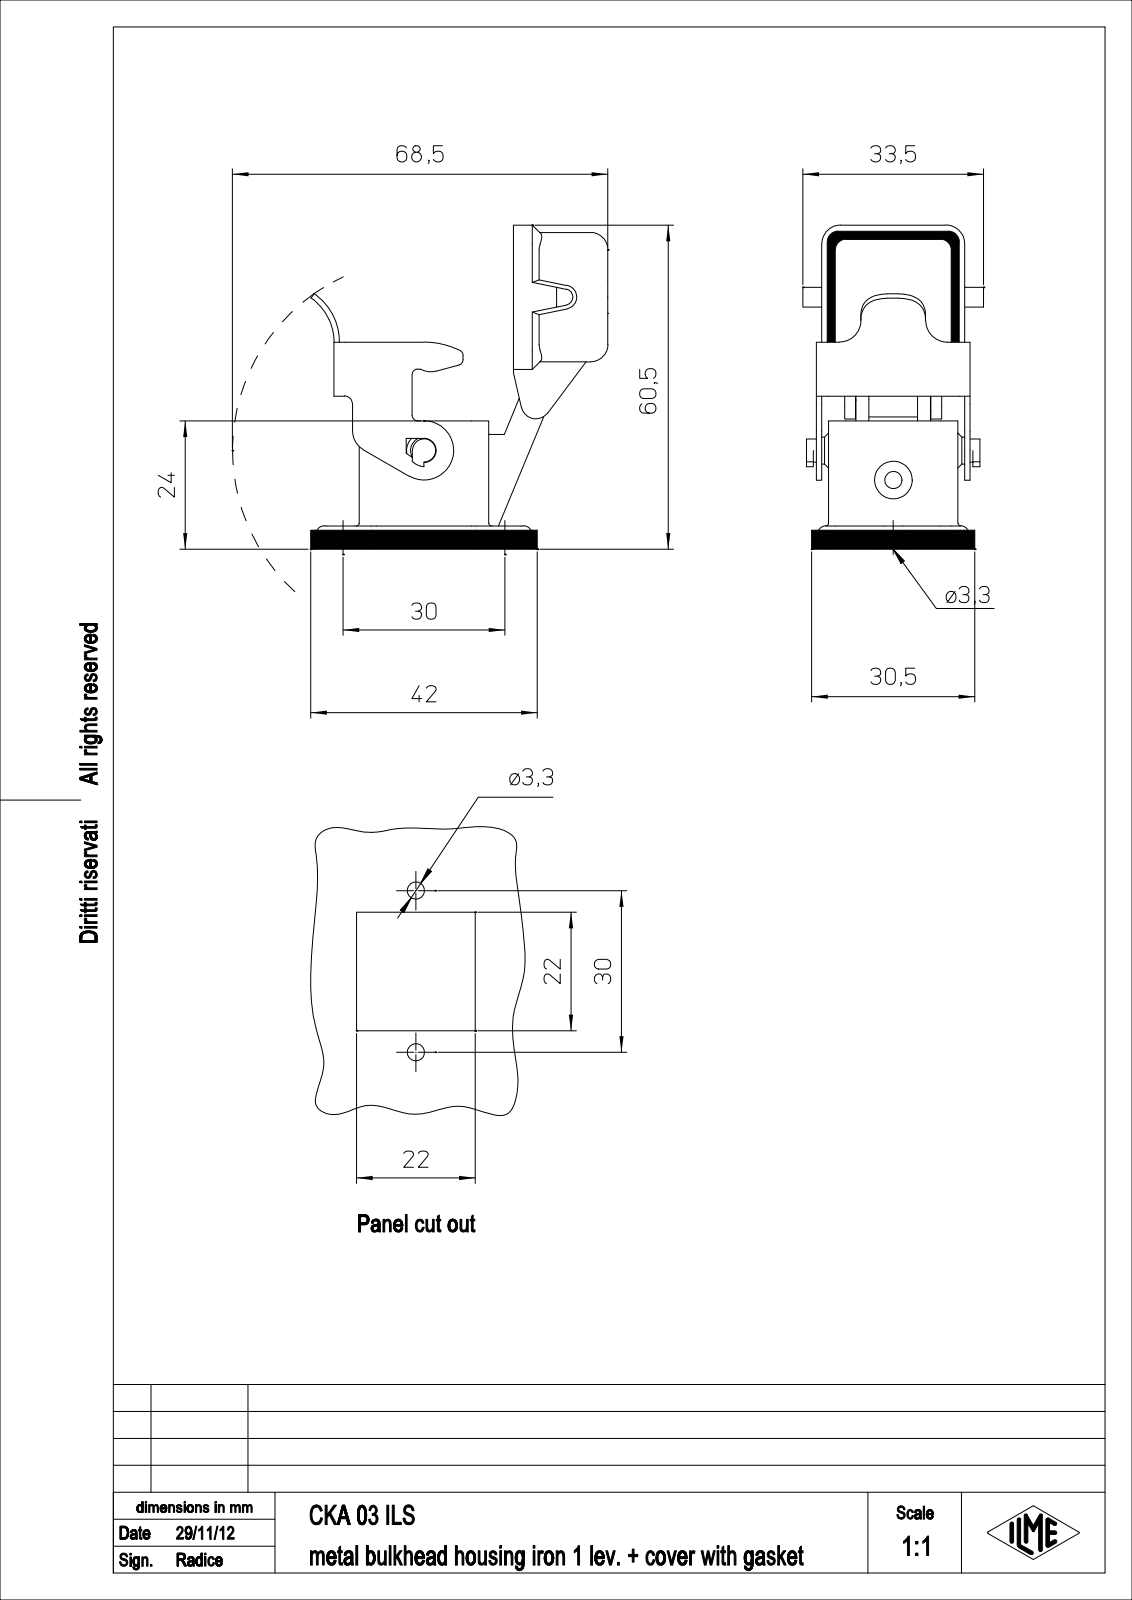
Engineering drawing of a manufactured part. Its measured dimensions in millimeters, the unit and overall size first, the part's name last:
Units: millimetres
Overall size (bounding box): 60.15 × 55.4 × 33.5
Round holes (diameter × count): ⌀3.3 ×2, ⌀3.2 ×1, ⌀7 ×1
Round bosses / shafts (diameter × count): ⌀5 ×1, ⌀4.3 ×1, ⌀4.22 ×1, ⌀2 ×1
Partial cylindrical surfaces — rounded edges, fillets, slot ends (radius × count): R2 ×22, R0.2 ×15, R3.2 ×12, R1.5 ×8, R1 ×6, R6 ×6, R0.5 ×4, R3.5 ×4
Main face-to-face distances: 1.25, 1, 24, 25.25, 2.25, 26.25, 27.5, 1.2, 22.8, 2
Hole centre spacings: 30
Volume: 10 284 mm³ · Surface area: 13 340 mm²
Bodies: 1 solid, 331 faces (167 planar, 133 cylindrical, 31 other)
Part name (STEP PRODUCT): CKA_03_ILS
STEP written by: Creo Elements/Direct Modeling 18.0B 02-Dec-2011 (C) Parametric Technology GmbH (AUTOMOTIVE_DESIGN)
